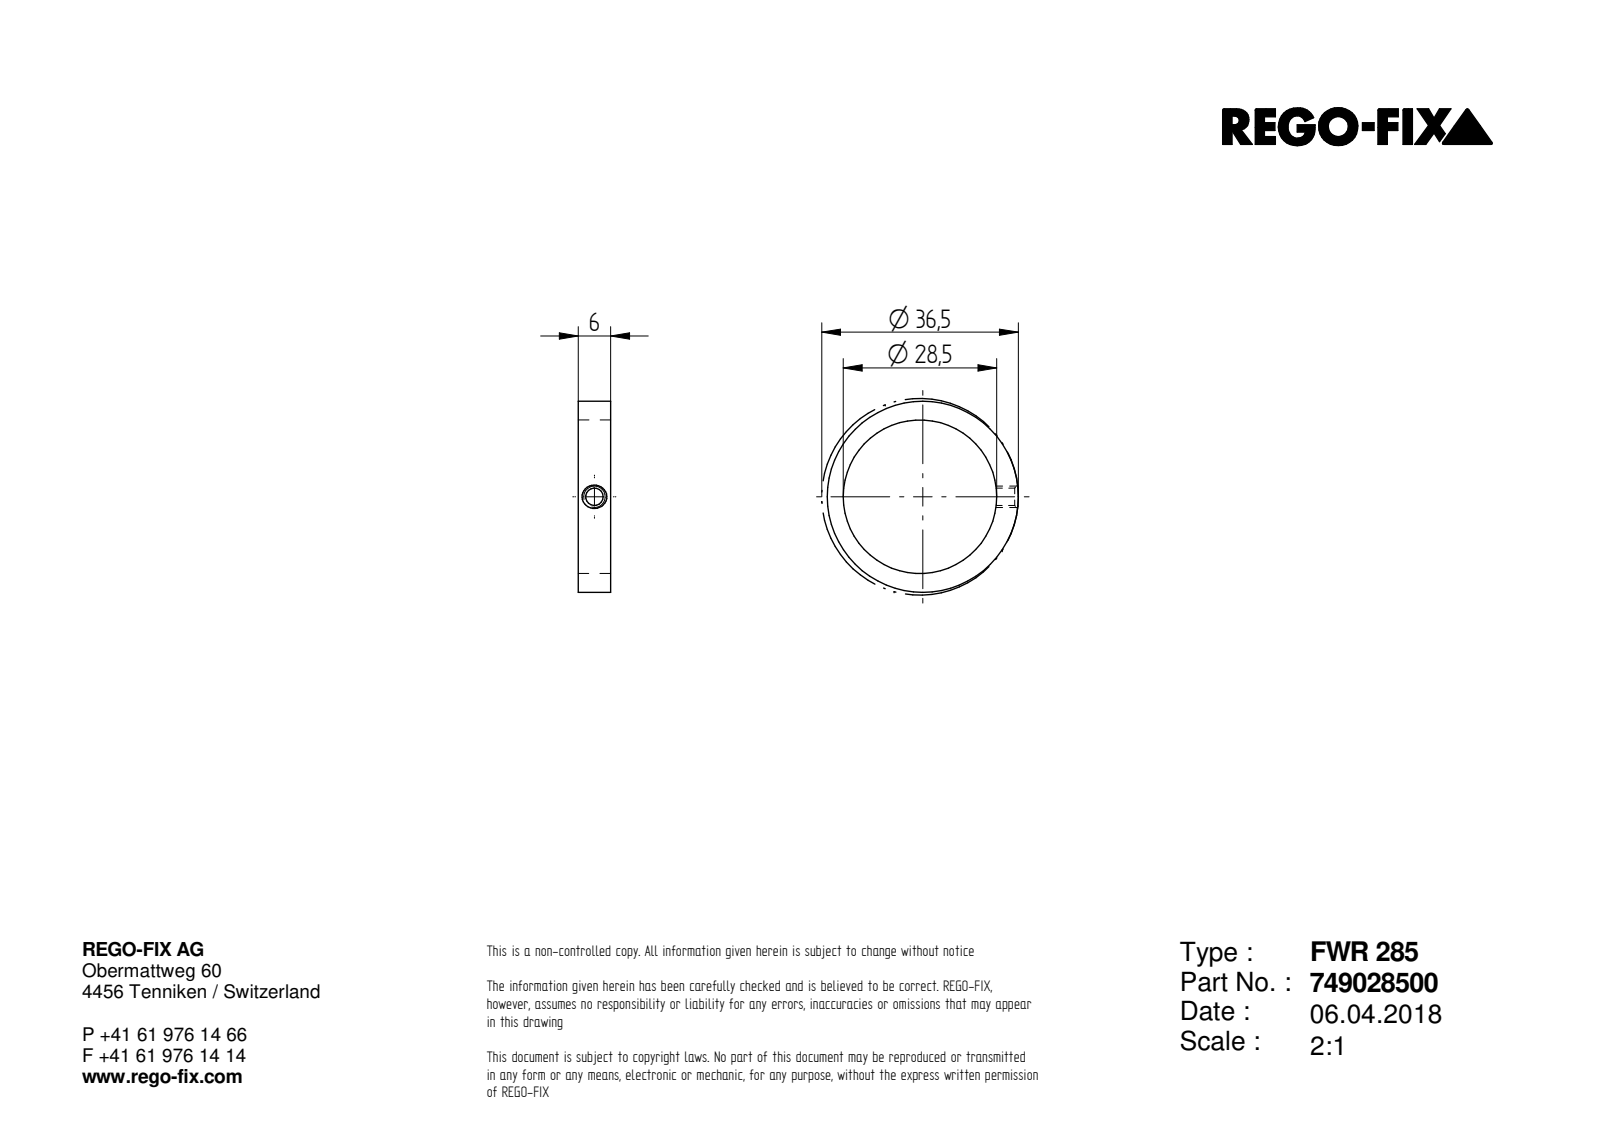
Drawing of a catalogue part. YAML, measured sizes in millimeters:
step_written_by: "Unknown (AUTOMOTIVE_DESIGN)"
units: millimeters
bodies: {solids: 1, faces: 6, planar: 2, cylindrical: 3, other: 1}
overall_size: [35.45, 35.45, 6]
volume: 2059
surface_area: 1924
round_holes:
  - {diameter: 3.24, count: 1}
  - {diameter: 28.5, count: 1}
round_bosses_or_shafts:
  - {diameter: 35.45, count: 1}
face_to_face_distances: [6]
